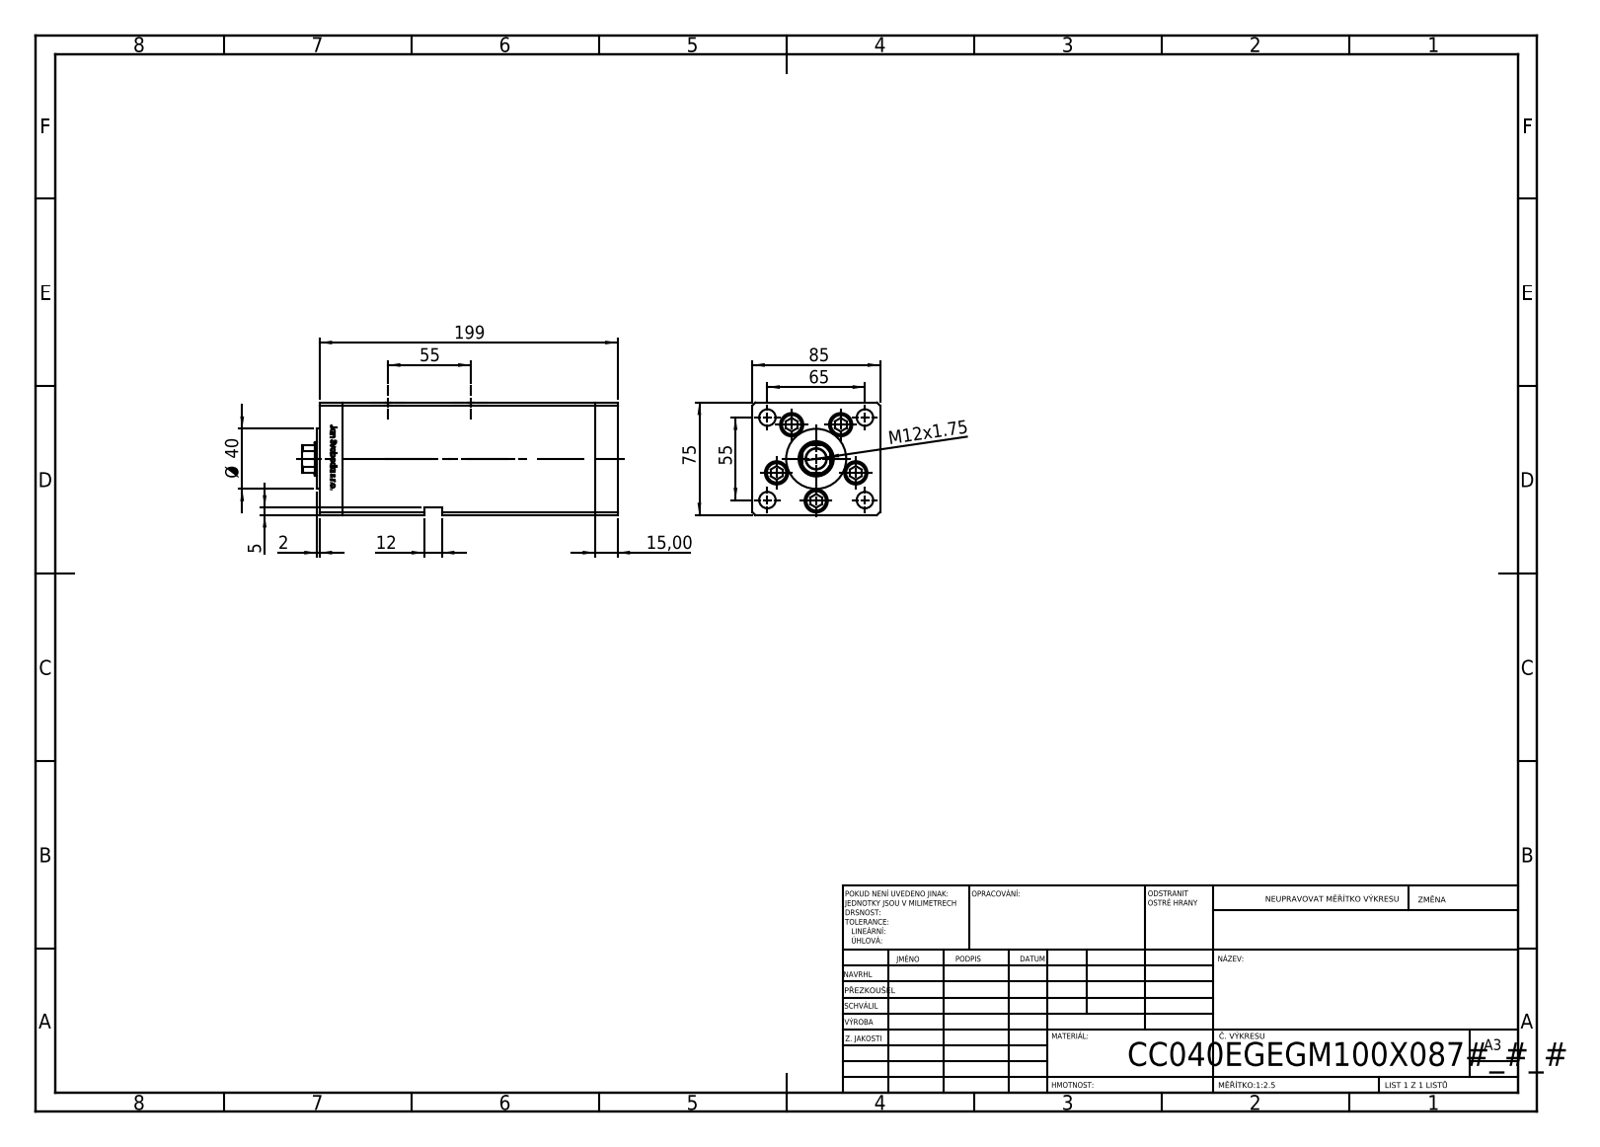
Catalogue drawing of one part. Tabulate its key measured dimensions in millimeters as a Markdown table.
| quantity | value |
| --- | --- |
| part name | V220C_FRONT_E; V220C BACK_E; ALLEN BOLT; V220C_E MIDDLE (+1 more) |
| STEP written by | SolidWorks 2019 (CONFIG_CONTROL_DESIGN) |
| units | millimeters |
| bodies | 14 solids, 1214 faces (475 planar, 165 cylindrical, 574 other) |
| overall size | 210 × 85 × 75 |
| volume | 1 076 000 mm³ |
| surface area | 182 851 mm² |
| round holes (diameter × count) | 11 × 9, 15.5 × 5, 10.5 × 4, 16.5 × 4, 2 × 2, 13.16 × 2, 13.5 × 1, 22 × 1, 23.5 × 1 |
| round bosses / shafts (diameter × count) | 14.5 × 5, 8 × 5, 40 × 1 |
| partial cylindrical surfaces (radius × count) | 0.93 × 2, 10.5 × 1 |
| main face-to-face distances | 85, 75, 15, 168.5, 183.5, 198.5, 34.25, 68.5, 10.5, 19.25 |
| hole center spacings | 28, 42.57, 55, 65, 85.15, 16.86, 19.17, 32.33 |
